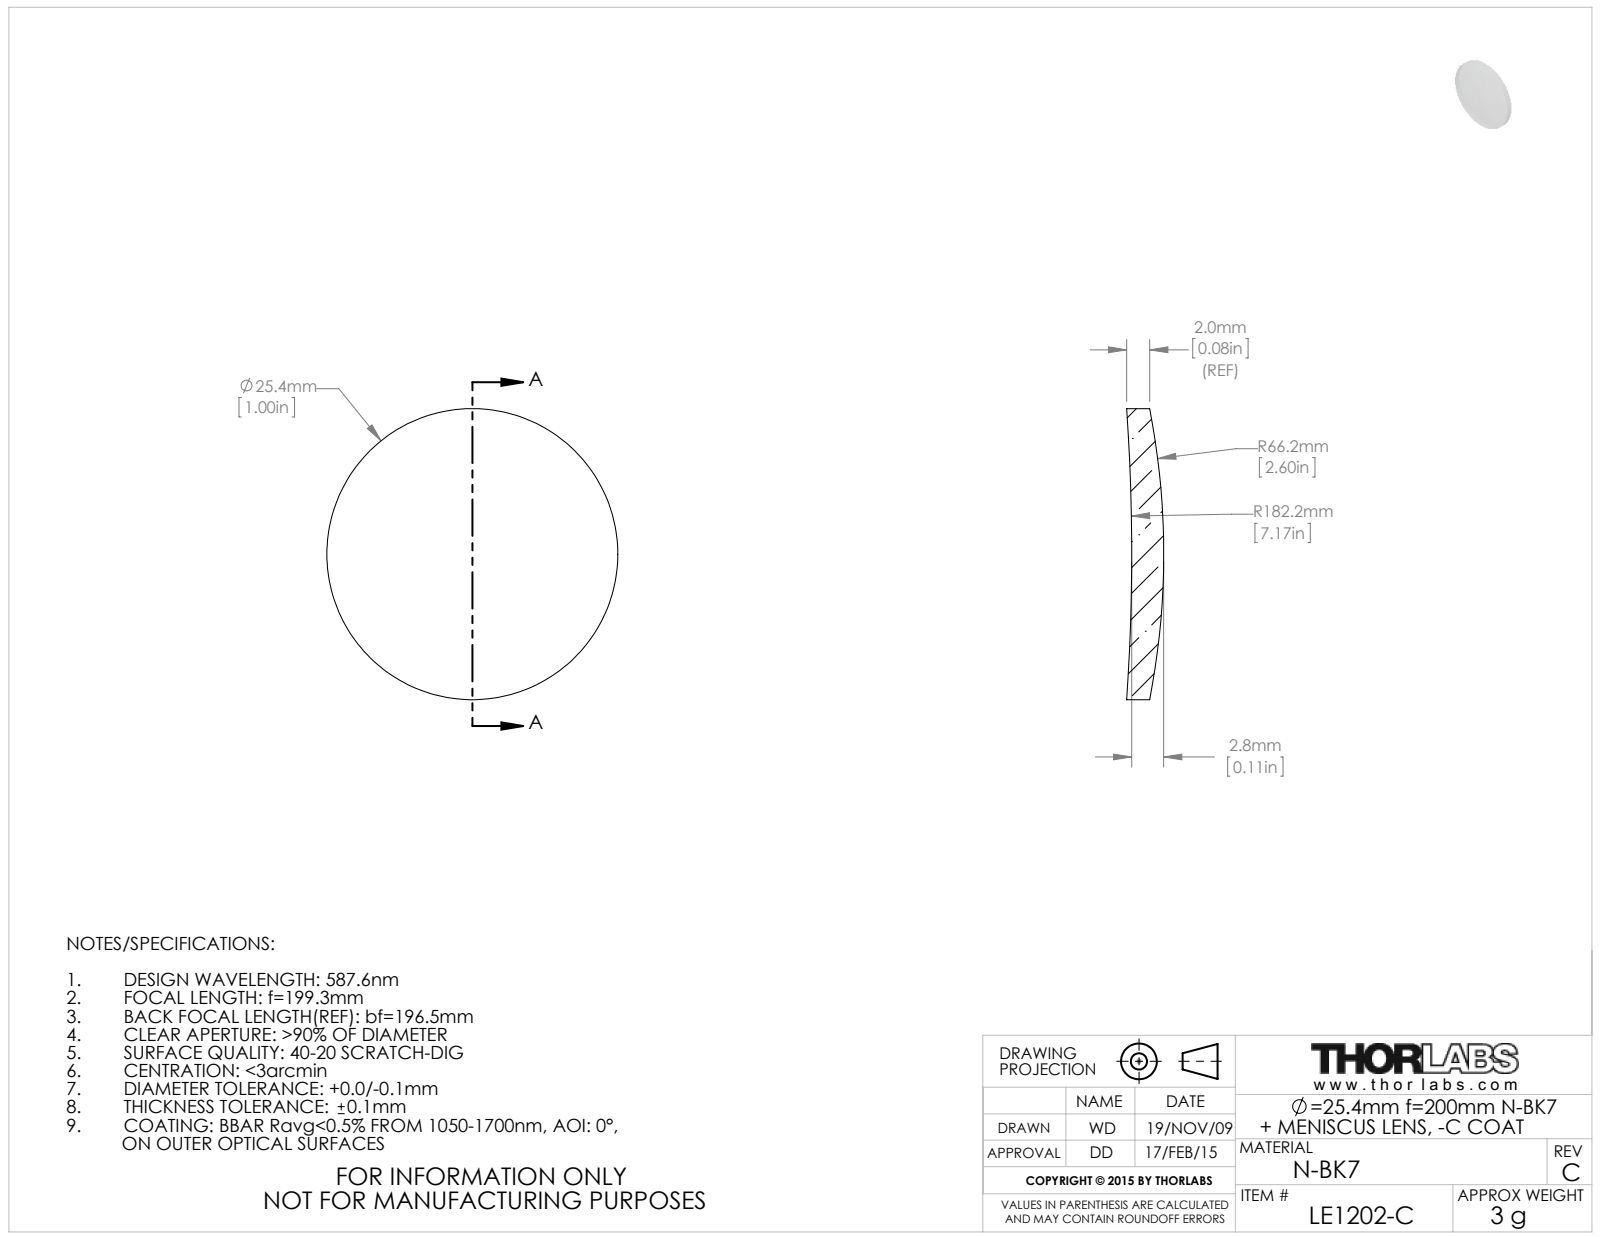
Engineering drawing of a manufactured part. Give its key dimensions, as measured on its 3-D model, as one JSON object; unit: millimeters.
{"part_name": "4853-E0W", "step_written_by": "SolidWorks 2009 (AUTOMOTIVE_DESIGN)", "units": "millimeters", "bodies": {"solids": 1, "faces": 6, "planar": 0, "cylindrical": 2, "other": 4}, "overall_size": [25.4, 25.4, 3.23], "volume_mm3": 1215, "surface_area_mm2": 1179, "round_bosses_or_shafts": [[25.4, 1]]}
